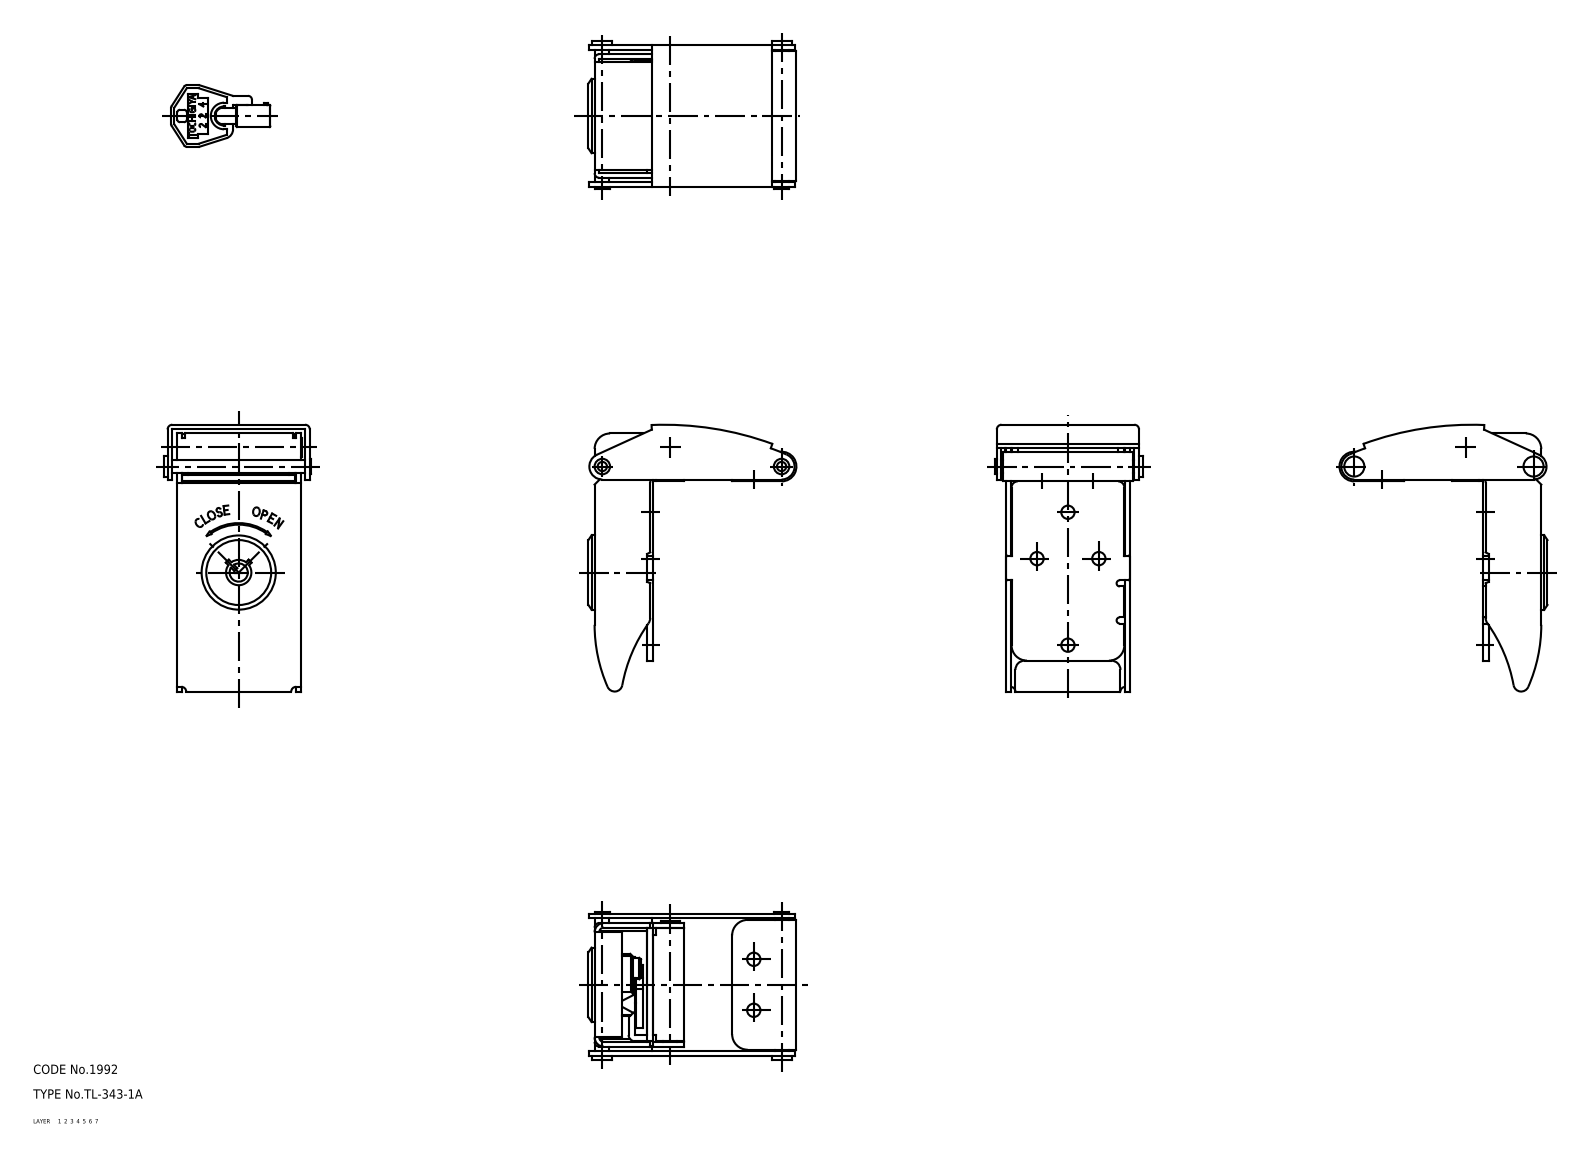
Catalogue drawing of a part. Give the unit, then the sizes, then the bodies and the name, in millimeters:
Units: millimetres
Overall size (bounding box): 122.3 × 86.32 × 47.7
Volume: 32 324 mm³ · Surface area: 35 636 mm²
Bodies: 6 solids, 335 faces (0 planar, 0 cylindrical, 335 other)
Part name (STEP PRODUCT): 67125712; 67125725; 67125738; 67125751 (+2 more)
STEP written by: CADfix (AUTOMOTIVE_DESIGN)
